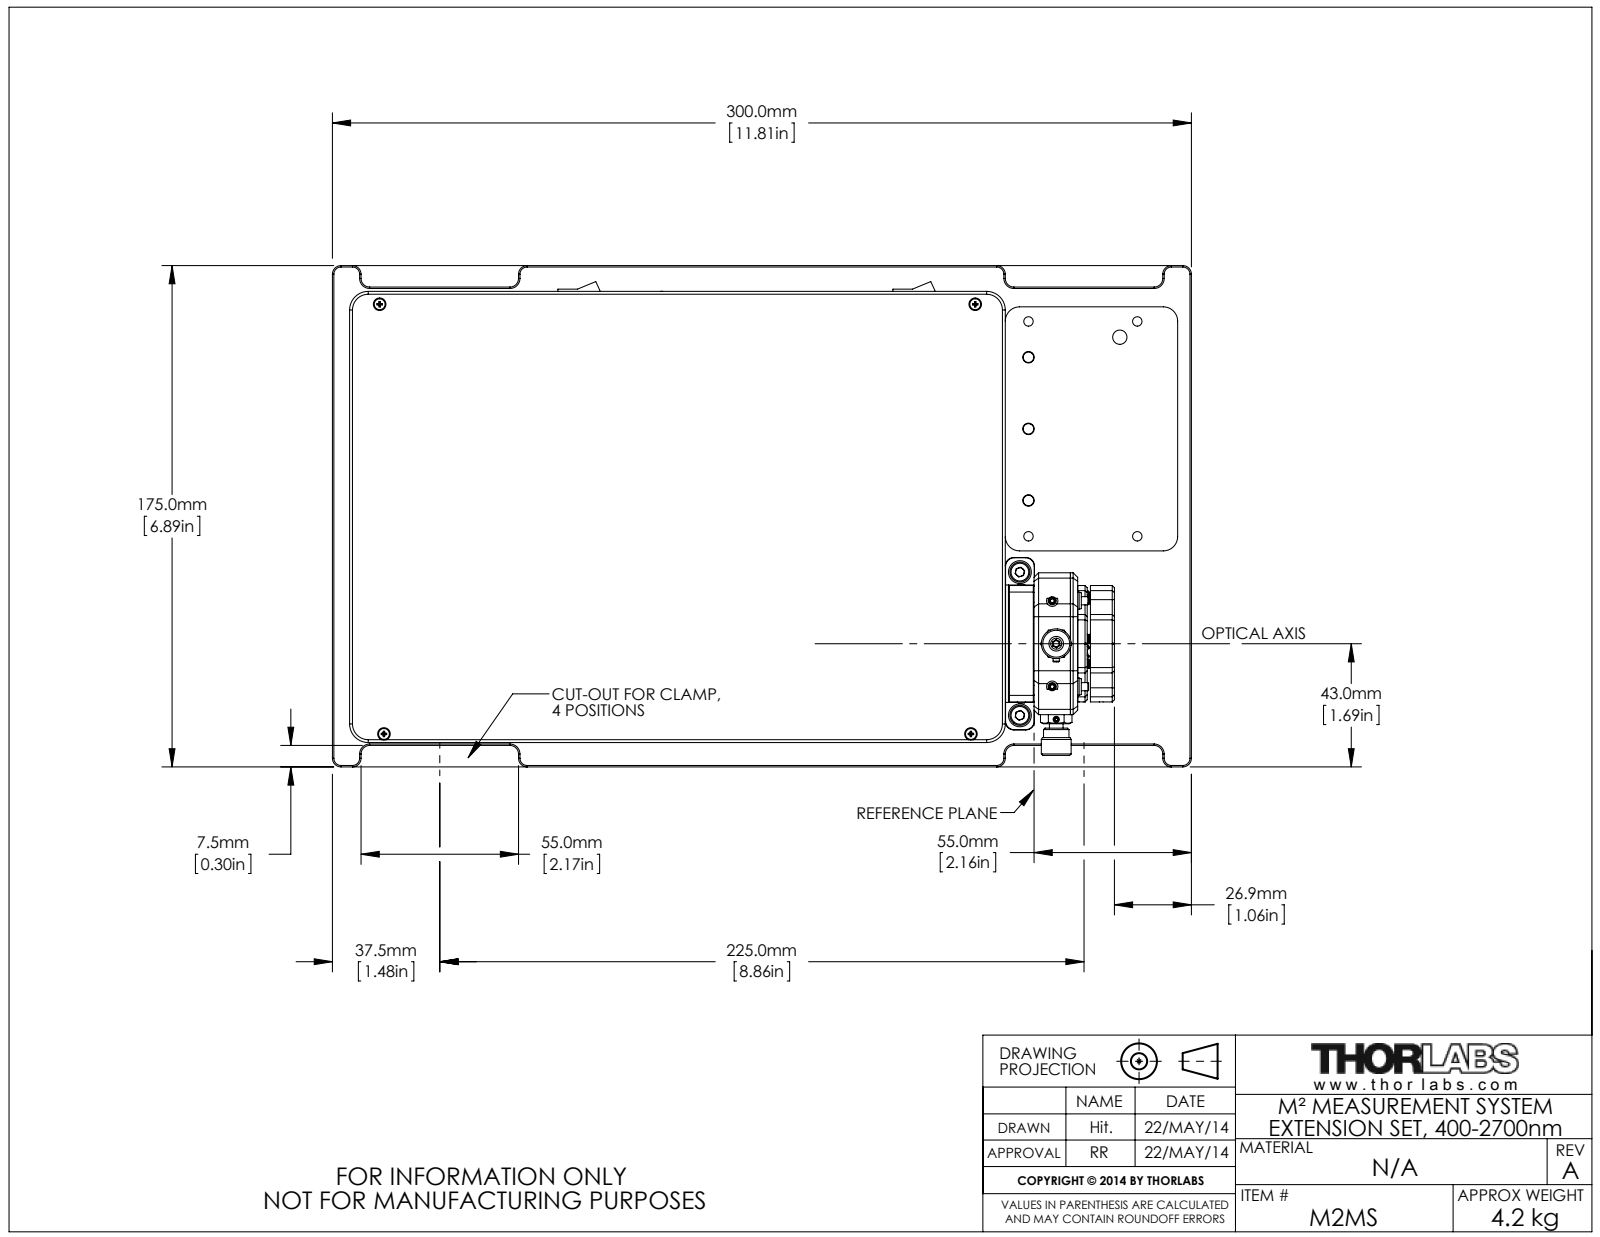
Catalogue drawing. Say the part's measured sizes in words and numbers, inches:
The part is named "MTN003884-E0W". Its 3-D file was written by "SolidWorks 2013 (AUTOMOTIVE_DESIGN)". It is 0 solids with 19522 faces: 11034 planar, 4407 cylindrical and 4081 other. Overall it measures 11.811 by 6.89 by 4.29 inches. Round holes: 30 of diameter 0.036, 16 of diameter 0.032, 13 of diameter 0.063, 12 of diameter 0.07, 11 of diameter 0.087, 11 of diameter 0.157, 10 of diameter 0.024, 10 of diameter 0.073, 9 of diameter 0.13, 8 of diameter 0.089, 8 of diameter 0.173, 7 of diameter 0.047. Round bosses or shafts: 14 of diameter 0.043, 14 of diameter 0.039, 13 of diameter 0.079, 8 of diameter 0.15, 8 of diameter 0.063, 6 of diameter 0.112, 4 of diameter 0.236, 4 of diameter 0.197. Partial cylindrical surfaces (rounded edges, fillets, slot ends): 193 of radius 0.006, 76 of radius 0.008, 69 of radius 0.004, 57 of radius 0.02, 50 of radius 0.118, 43 of radius 0.012, 36 of radius 0.039, 22 of radius 0.01. The main face-to-face distances are 0.118, 3.571, 3.453, 2.618, 2.736, 0.059, 0.835, 0.236, 8.78, 0.598. The hole center spacings are 1.567, 0.635, 1.181, 0.037, 0.232, 0.25, 0.352, 0.694.
